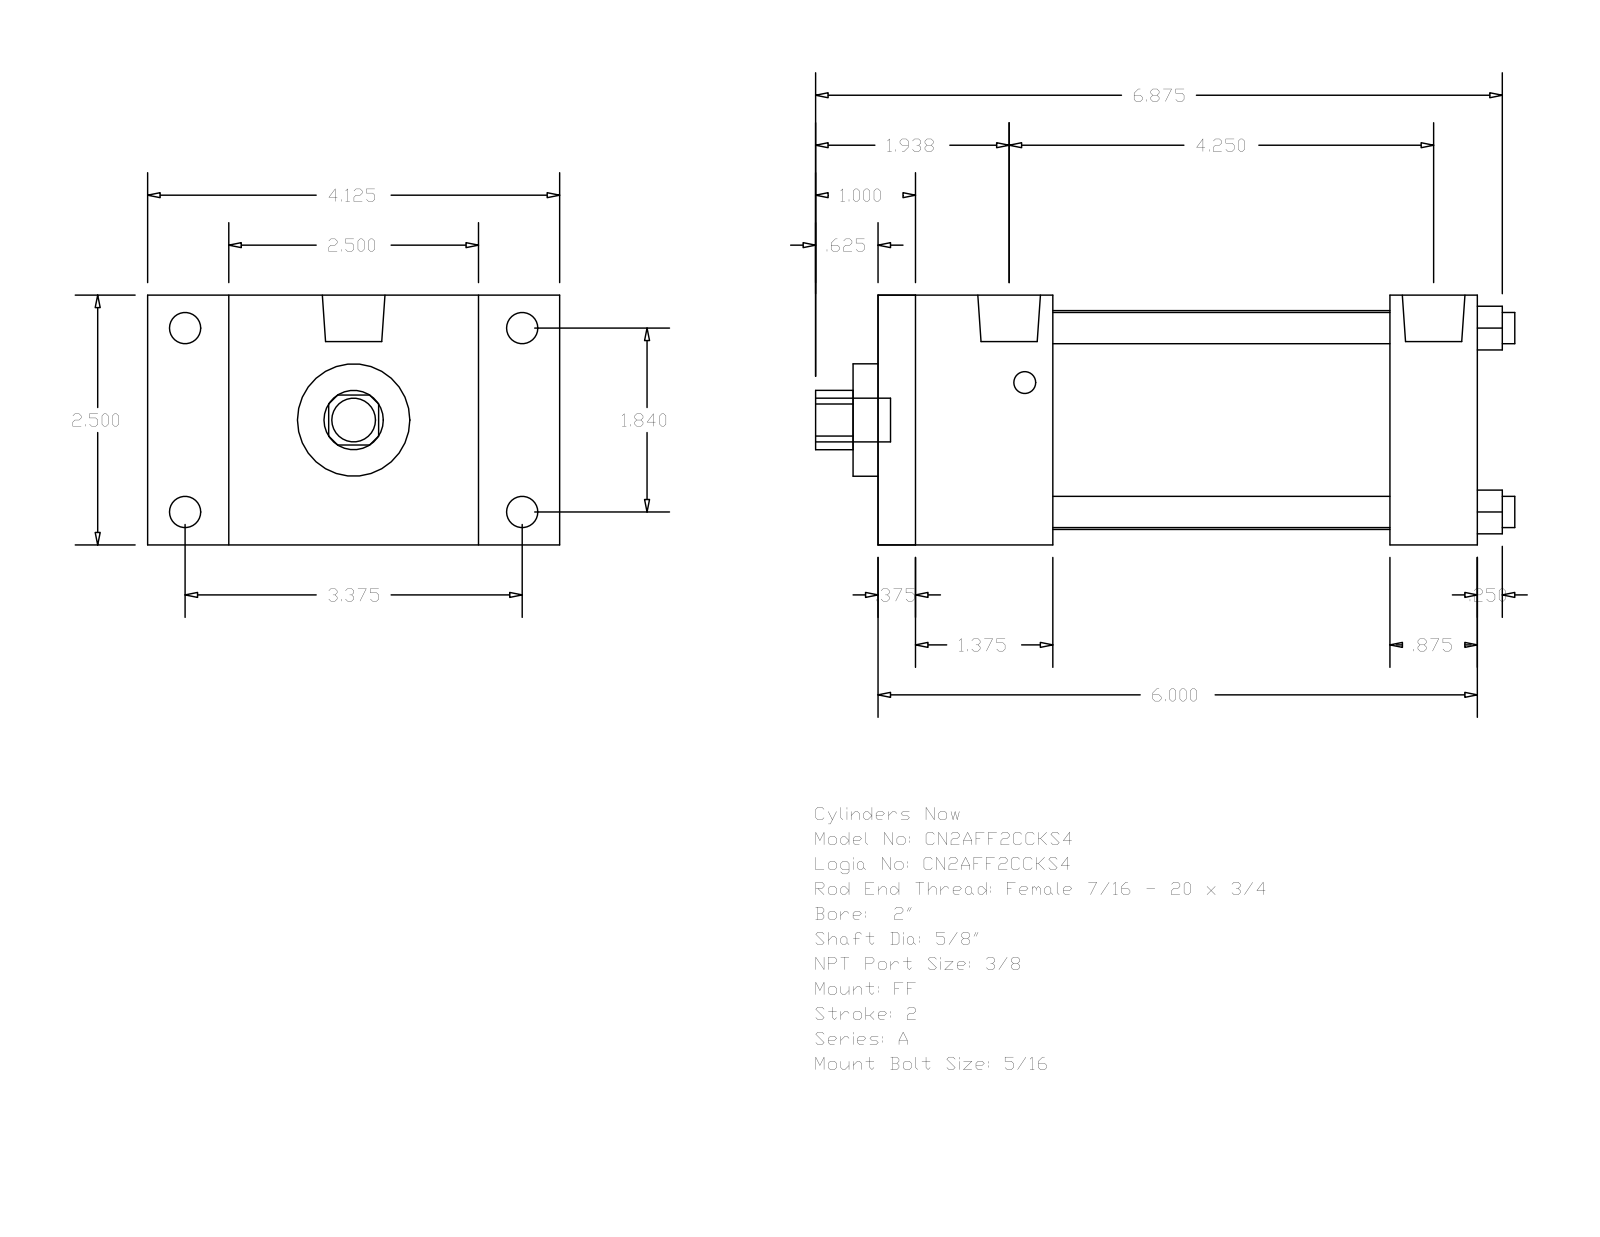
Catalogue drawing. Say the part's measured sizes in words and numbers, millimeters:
The part is named "A_FF__0200_0.625". Its 3-D file was written by "GSSL Pune (CONFIG_CONTROL_DESIGN)". It is 0 solids with 92 faces: 64 planar, 28 cylindrical and 0 other. Overall it measures 177.8 by 104.78 by 63.5 millimeters. Round holes: 4 of diameter 7.94, 1 of diameter 15.88, 1 of diameter 28.57, 1 of diameter 55.63. Round bosses or shafts: 4 of diameter 7.94, 4 of diameter 5.56, 2 of diameter 15.93, 1 of diameter 11.11. Partial cylindrical surfaces (rounded edges, fillets, slot ends): 1 of radius 7.54. The main face-to-face distances are 63.5, 152.4, 9.52, 142.88, 44.45, 130.17, 34.93, 120.65, 85.72, 107.95. The hole center spacings are 33.05, 46.74, 66.1.
